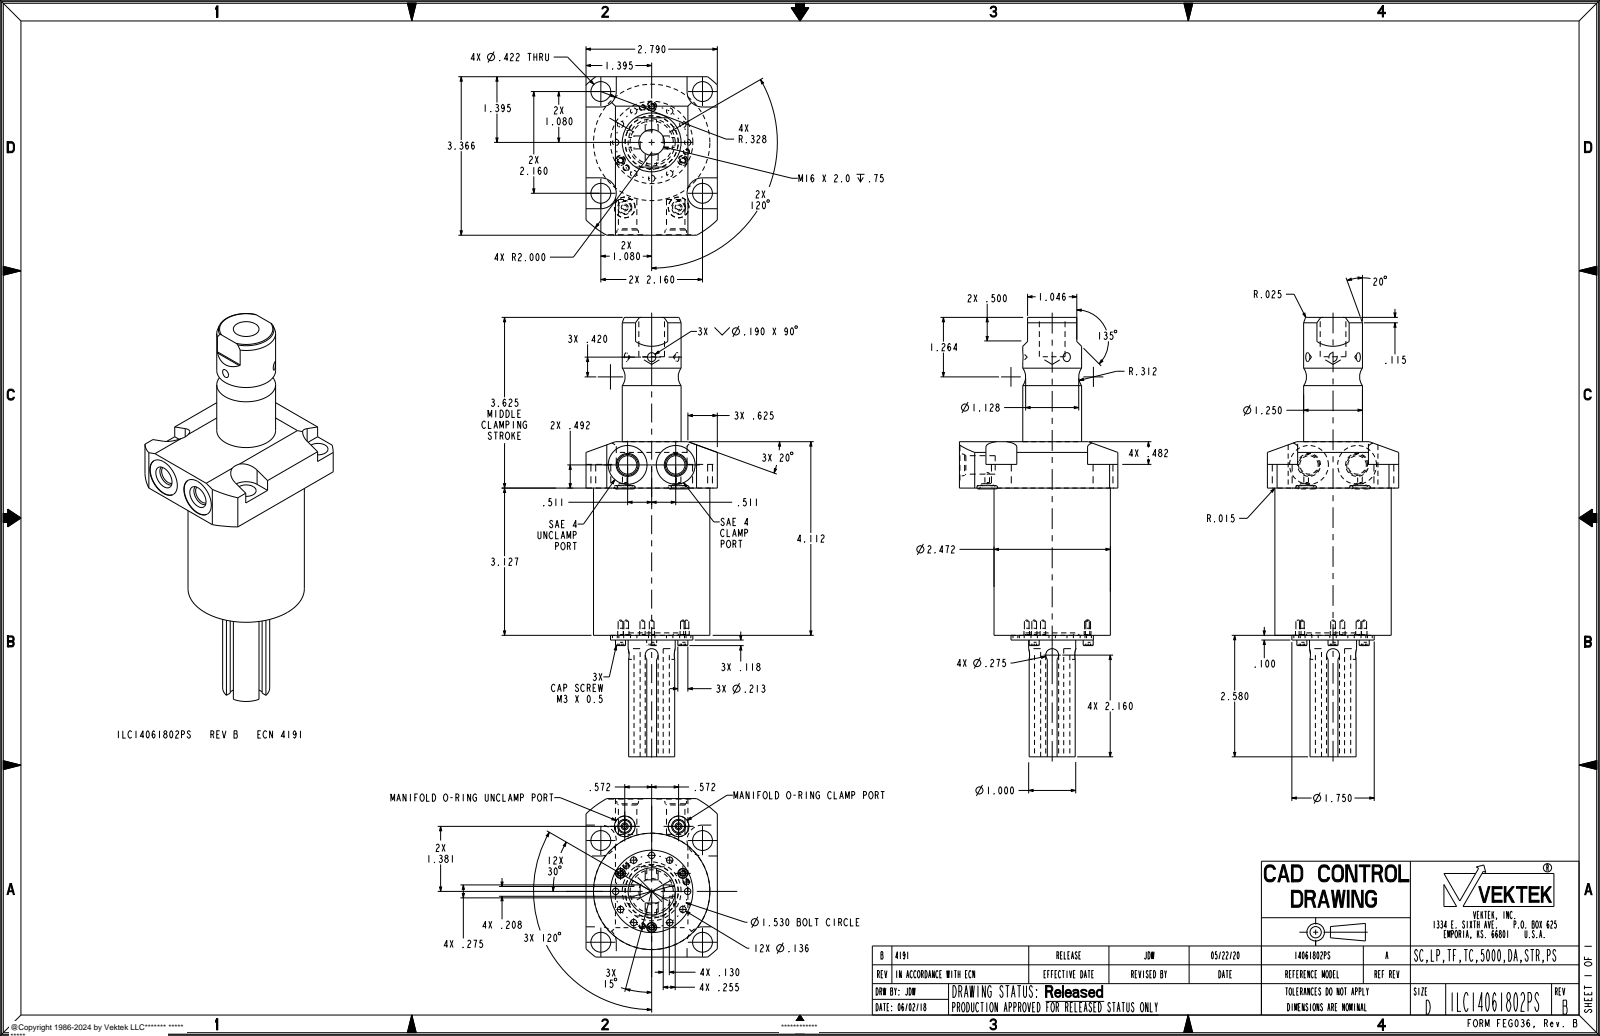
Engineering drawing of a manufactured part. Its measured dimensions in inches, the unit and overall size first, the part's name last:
Units: inches
Overall size (bounding box): 9.332 × 3.366 × 2.79
Round holes (diameter × count): ⌀0.136 ×12, ⌀0.1 ×6, ⌀0.422 ×4, ⌀0.098 ×2, ⌀0.256 ×2, ⌀0.392 ×2, ⌀0.438 ×2, ⌀0.825 ×2, ⌀0.546 ×1, ⌀1.13 ×1
Round bosses / shafts (diameter × count): ⌀0.118 ×6, ⌀0.213 ×3, ⌀2.472 ×1, ⌀1.75 ×1, ⌀1.25 ×1, ⌀1 ×1, ⌀0.917 ×1
Partial cylindrical surfaces — rounded edges, fillets, slot ends (radius × count): R0.328 ×4, R0.03 ×2, R0.138 ×2, R2 ×1
Main face-to-face distances: 3.127, 0.985, 4.112, 0.107, 0.382, 0.141, 0.349, 0.033, 0.241, 2.79
Hole centre spacings: 0.765, 1.325, 0.396, 0.765, 0.813, 1.082, 1.125, 1.478
Volume: 27 in³ · Surface area: 86.07 in²
Bodies: 3 solids, 295 faces (117 planar, 112 cylindrical, 66 other)
Part name (STEP PRODUCT): ILC14061802PS
STEP written by: PRO/ENGINEER BY PARAMETRIC TECHNOLOGY CORPORATION, 2013320 (AUTOMOTIVE_DESIGN)
